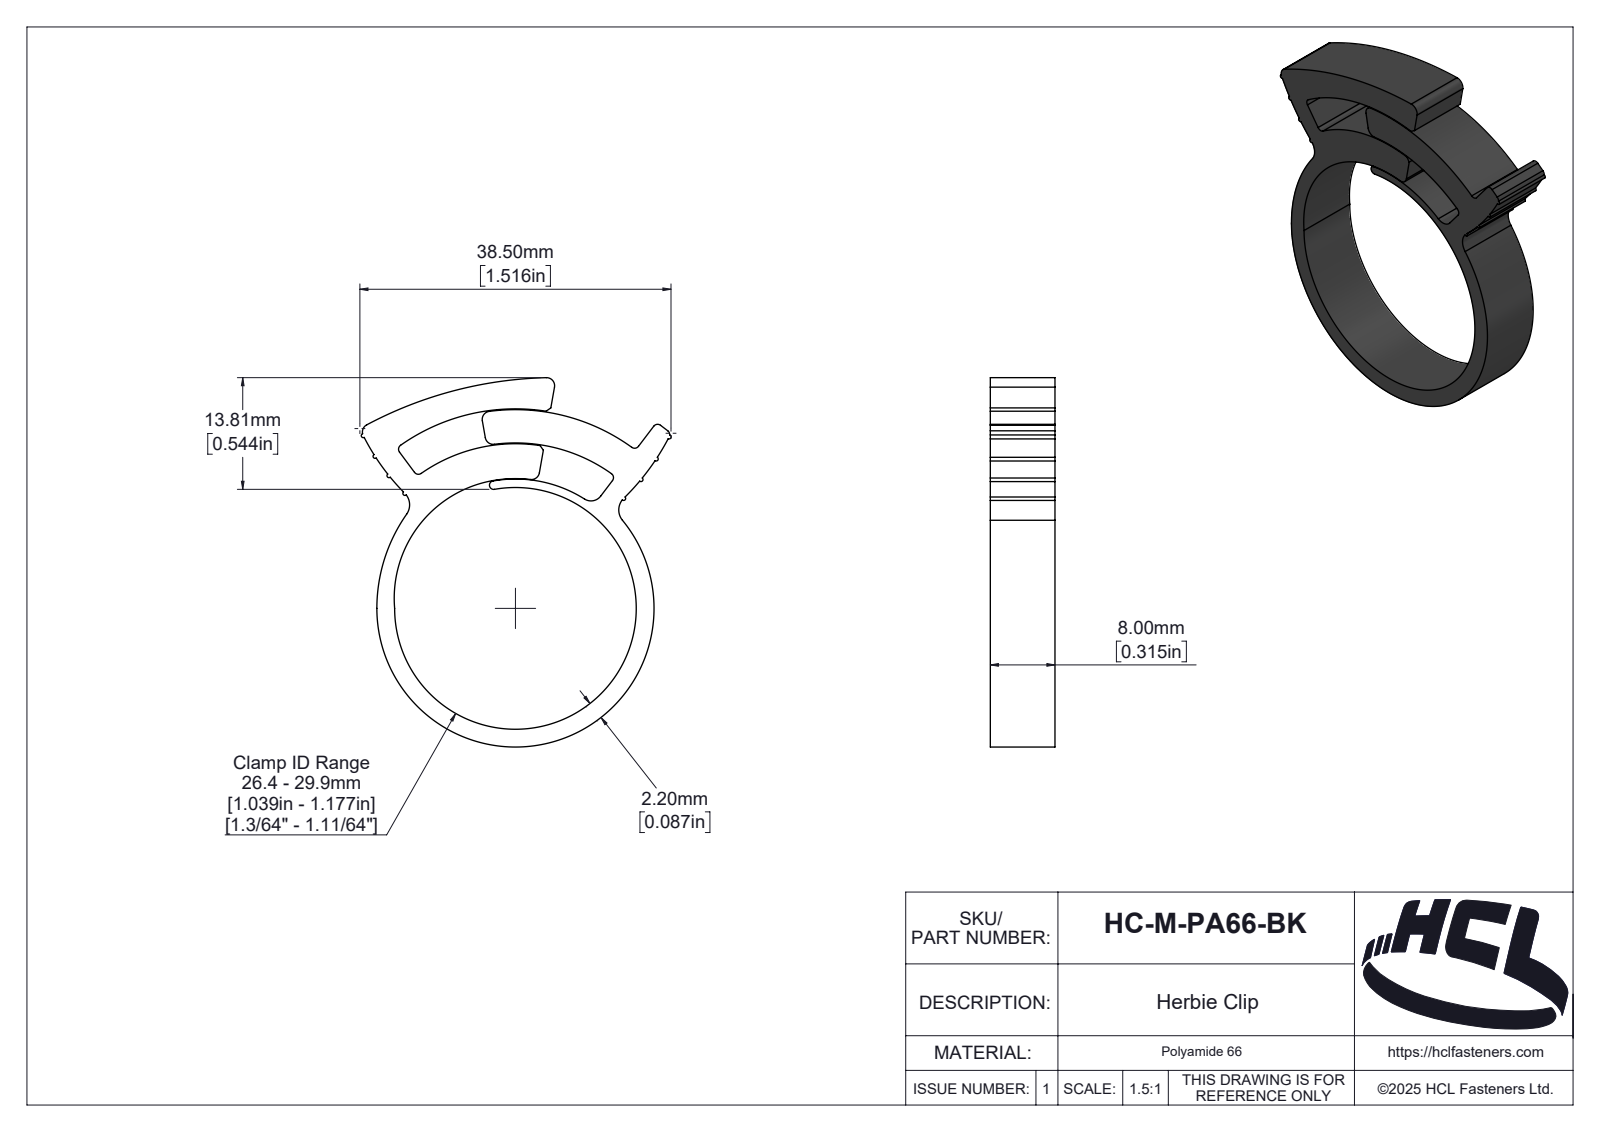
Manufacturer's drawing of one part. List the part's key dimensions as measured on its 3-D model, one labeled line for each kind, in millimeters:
Part name (STEP PRODUCT): HC-M-PA66-BK
STEP written by: SolidWorks 2025 (AUTOMOTIVE_DESIGN)
Units: millimetres
Bodies: 1 solid, 162 faces (13 planar, 100 cylindrical, 49 other)
Overall size (bounding box): 45.69 × 38.35 × 8
Volume: 3 745 mm³ · Surface area: 3 689 mm²
Partial cylindrical surfaces — rounded edges, fillets, slot ends (radius × count): R0.25 ×8, R0.6 ×6, R1 ×5, R2 ×2, R0.17 ×1, R0.53 ×1, R0.67 ×1, R0.84 ×1
Main face-to-face distances: 8
